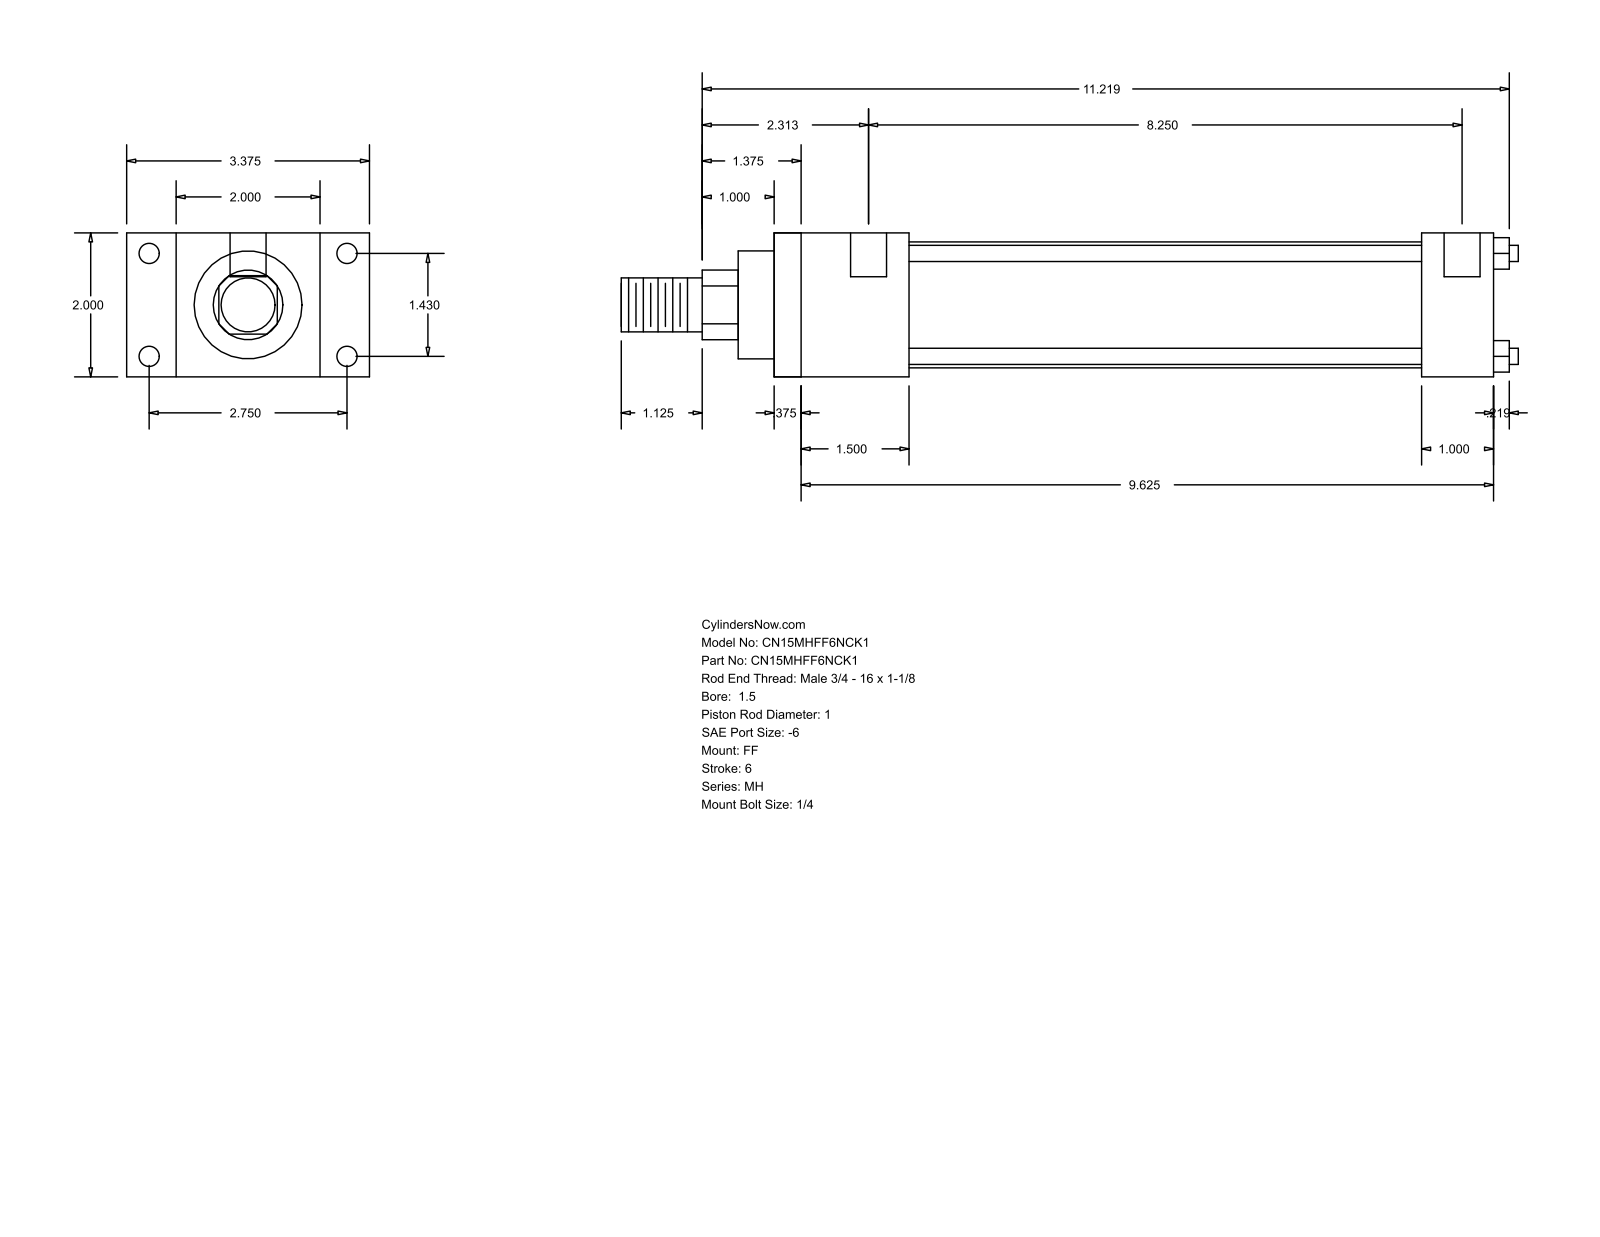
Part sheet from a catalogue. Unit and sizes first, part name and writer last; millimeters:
Units: millimetres
Overall size (bounding box): 316.71 × 85.72 × 50.8
Round holes (diameter × count): ⌀5.56 ×4, ⌀7.14 ×4, ⌀12.7 ×2
Round bosses / shafts (diameter × count): ⌀5.71 ×4, ⌀44.45 ×1, ⌀38.1 ×1, ⌀25.4 ×1, ⌀19.05 ×1
Partial cylindrical surfaces — rounded edges, fillets, slot ends (radius × count): R12.29 ×1
Main face-to-face distances: 50.8, 254, 9.52, 244.48, 25.4, 17.46, 68.26, 47.63, 38.11, 206.37
Hole centre spacings: 36.32, 69.84, 78.72, 212.73, 3.18, 209.55
Bodies: 0 solids, 92 faces (64 planar, 28 cylindrical, 0 other)
Part name (STEP PRODUCT): MH_FF__0150_1
STEP written by: GSSL Pune (CONFIG_CONTROL_DESIGN)
